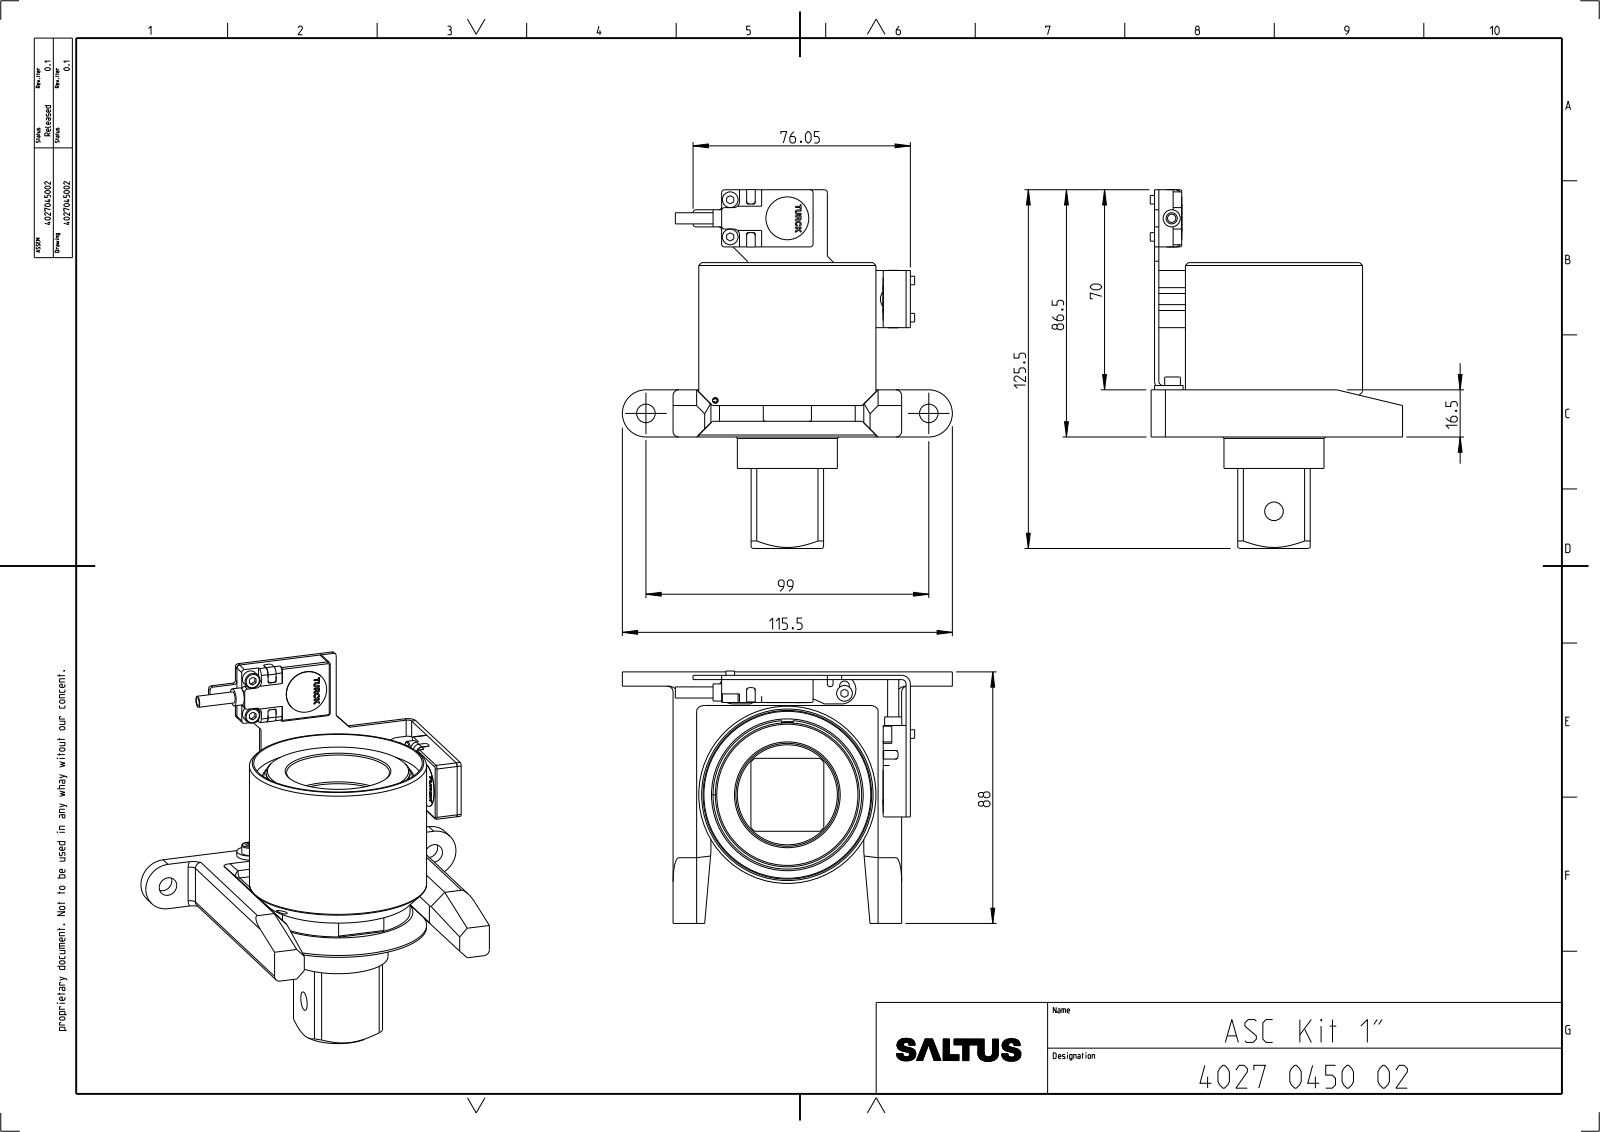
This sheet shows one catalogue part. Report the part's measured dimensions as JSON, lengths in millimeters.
{"part_name": "4027045250; 4027045260; 4027040210; 4027040211 (+8 more)", "step_written_by": "CREO PARAMETRIC BY PTC INC, 2022414 (CONFIG_CONTROL_DESIGN)", "units": "millimeters", "bodies": {"solids": 20, "faces": 737, "planar": 345, "cylindrical": 241, "other": 151}, "overall_size": [125.55, 115.5, 88.3], "volume_mm3": 204004, "surface_area_mm2": 83737, "round_holes": [[2.5, 6], [3, 6], [3.4, 4], [6.5, 4], [2.9, 2], [1.2, 1], [2, 1], [7.1, 1], [35, 1], [36, 1], [50.55, 1], [51.1, 1]], "round_bosses_or_shafts": [[5.5, 6], [15, 2], [6, 2], [3.9, 2], [62, 1], [58.4, 1], [50.4, 1]], "partial_cylinders_radius": [[1, 33], [2, 19], [0.5, 18], [0.3, 8], [1.7, 4], [2.05, 4], [1.5, 2], [3, 2]], "face_to_face_distances": [1.5, 16.5, 25.44, 2.7, 1.2, 8, 37.5, 3, 55.5, 54], "hole_center_spacings": [13, 40.75, 24.72, 26.17, 28.67, 37.67, 38.62, 40]}
